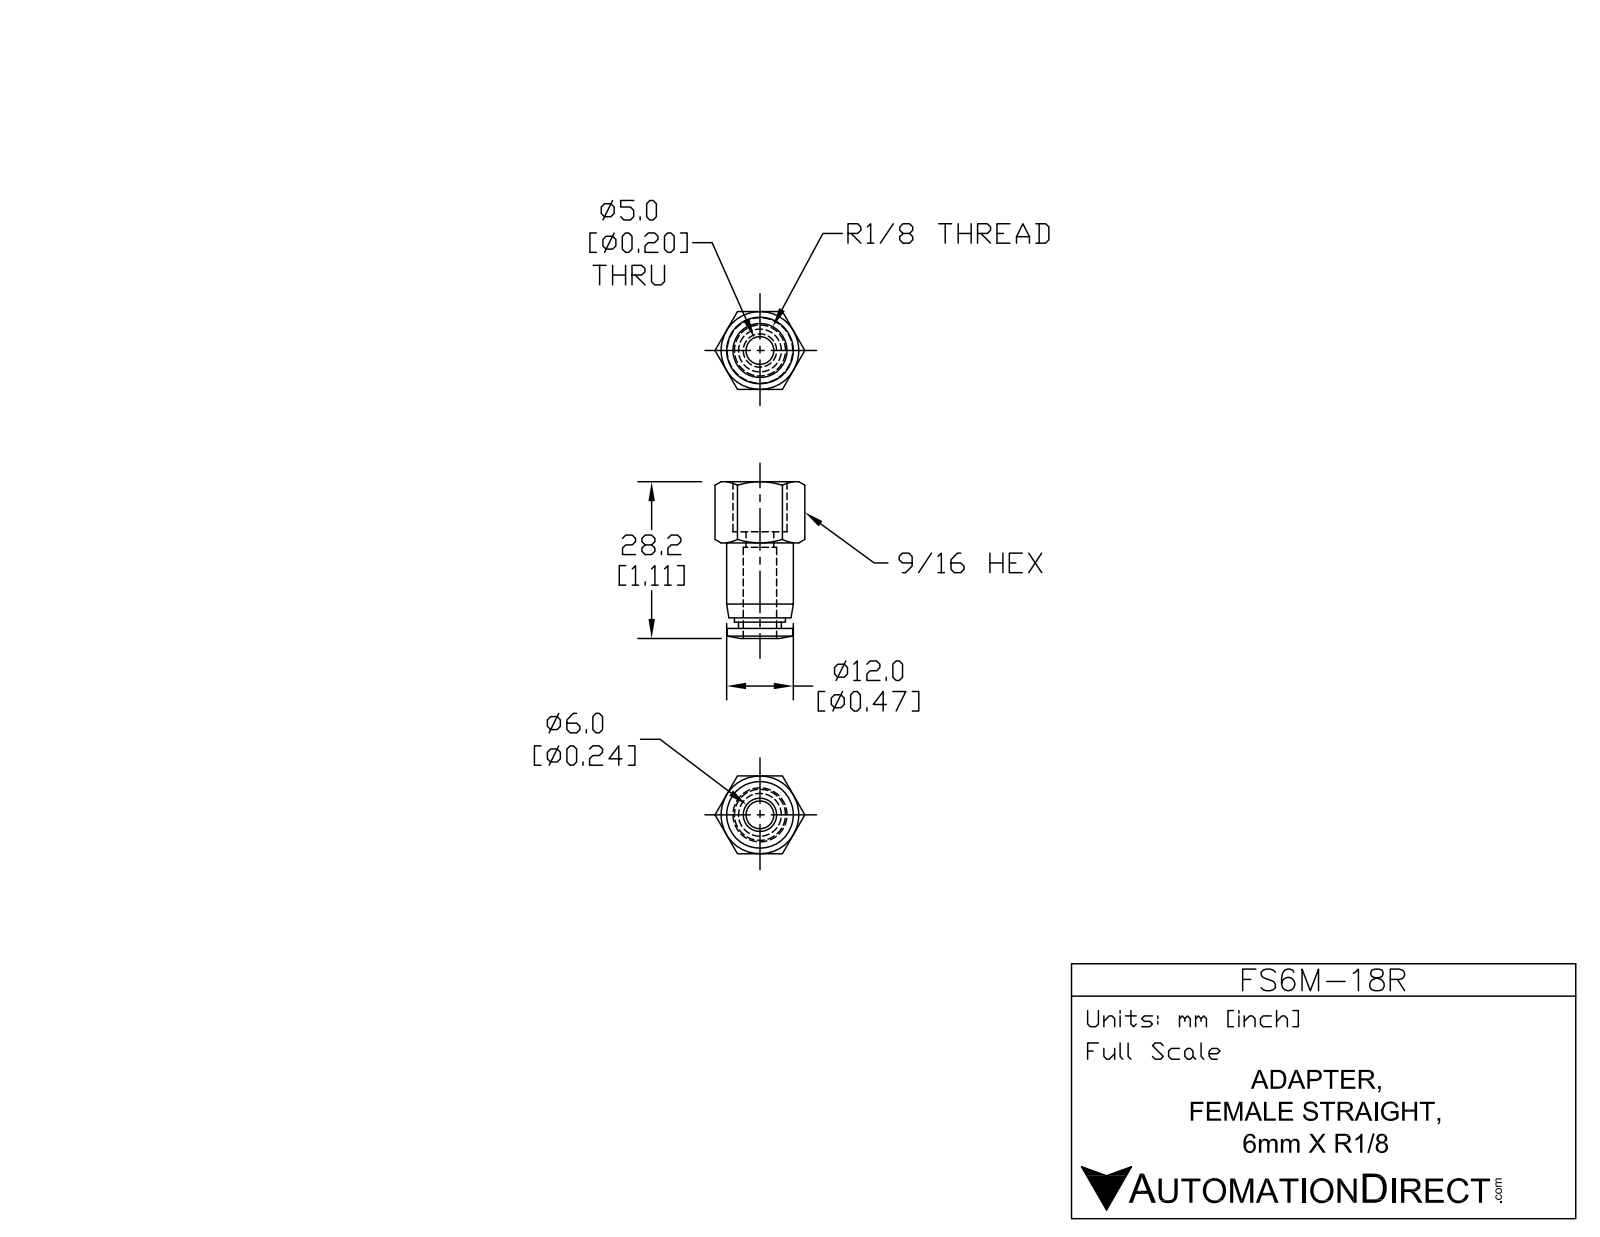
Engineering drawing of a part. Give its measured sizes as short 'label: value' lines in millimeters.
name: FS6M-18R
written by: SolidWorks 2015 (AUTOMOTIVE_DESIGN)
unit: mm
bodies: 1 solid, 48 faces (14 planar, 12 cylindrical, 22 other)
size: 28.2 × 16.2 × 14
volume: 2 460 mm³; area: 2 163 mm²
holes: 1× ⌀5, 1× ⌀6.3
bosses: 1× ⌀12, 1× ⌀11.8, 1× ⌀9.2, 1× ⌀7.7
face distances: 14, 26.4, 9, 17.4, 11, 2, 15.4, 24.5, 15.5, 13.5
